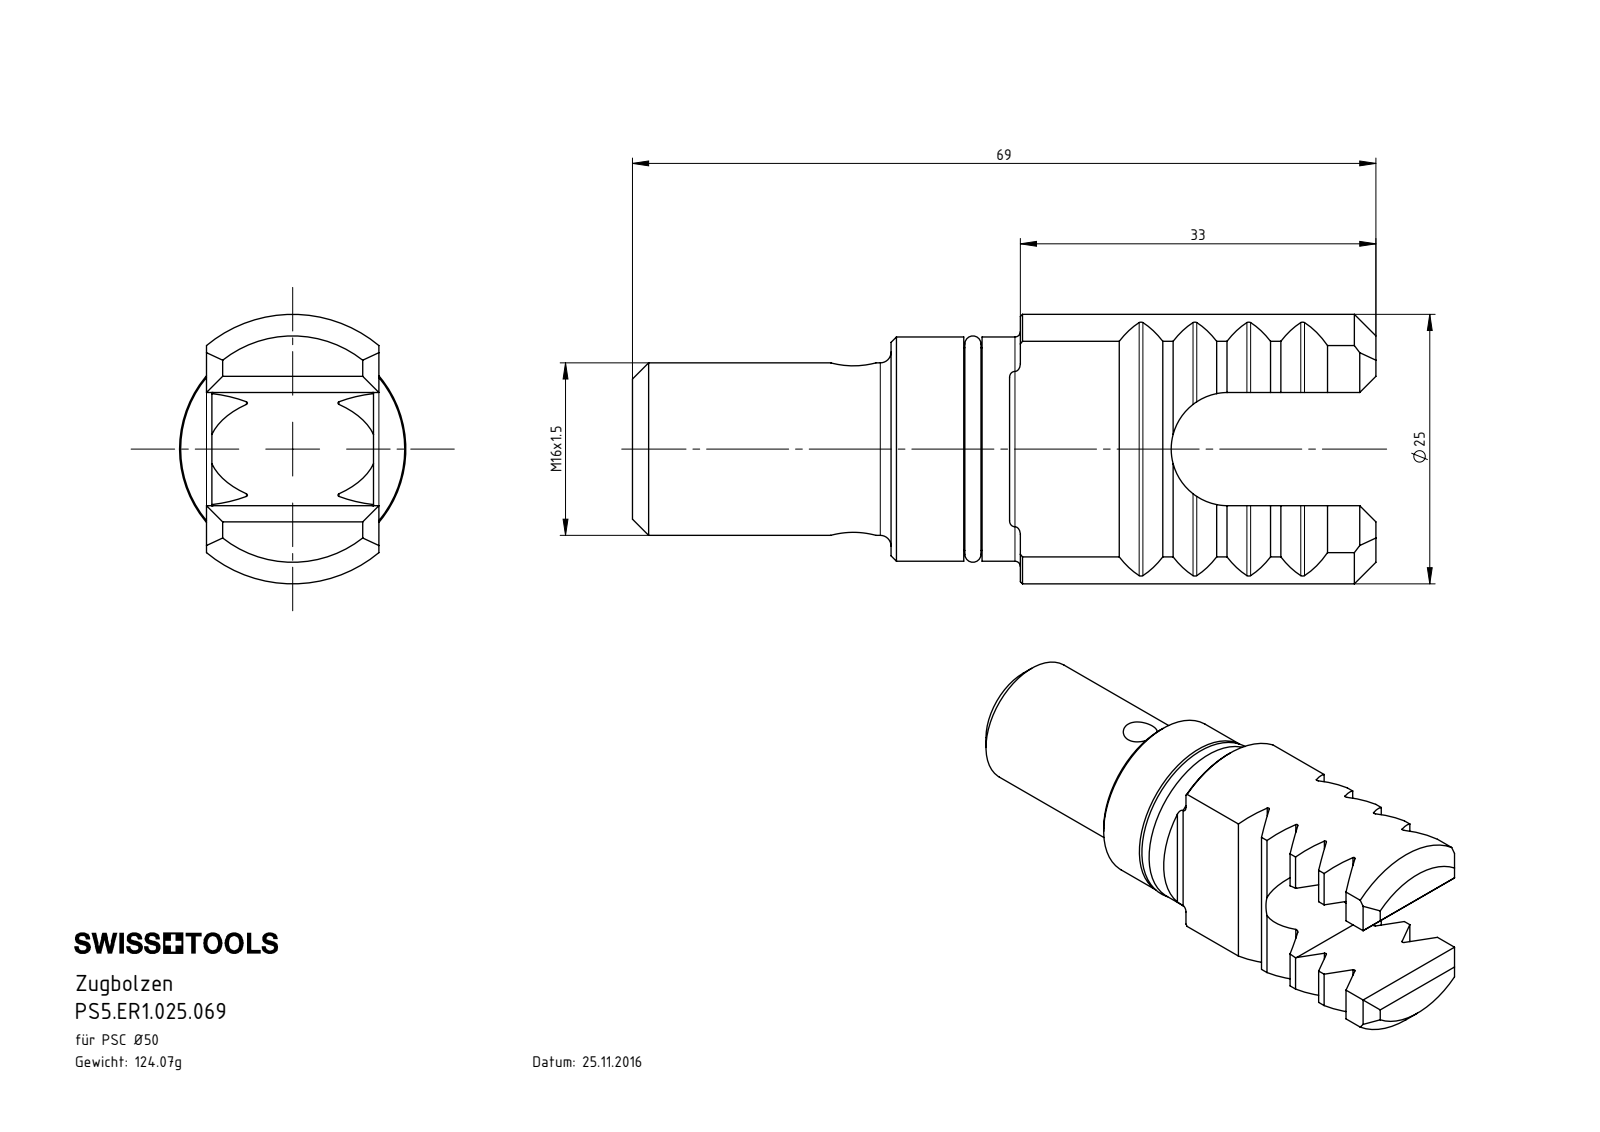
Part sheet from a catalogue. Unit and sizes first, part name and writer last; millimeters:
Units: millimetres
Overall size (bounding box): 69 × 25 × 21
Round holes (diameter × count): ⌀4.2 ×1, ⌀6 ×1
Round bosses / shafts (diameter × count): ⌀20.8 ×1, ⌀18.8 ×1, ⌀16 ×1
Partial cylindrical surfaces — rounded edges, fillets, slot ends (radius × count): R0.2 ×8, R0.5 ×2, R5.25 ×1, R12.5 ×1
Main face-to-face distances: 4.33, 4, 8.66, 8.33, 0.33, 15, 12.99, 4.66, 12.66, 10.5
Volume: 15 899 mm³ · Surface area: 6 347 mm²
Bodies: 2 solids, 119 faces (62 planar, 34 cylindrical, 23 other)
Part name (STEP PRODUCT): PS5-ER1.025.069_A; DIN 3771 - 18x1.5; PS5-ER1.025.069
STEP written by: SolidWorks 2017 (AUTOMOTIVE_DESIGN)
